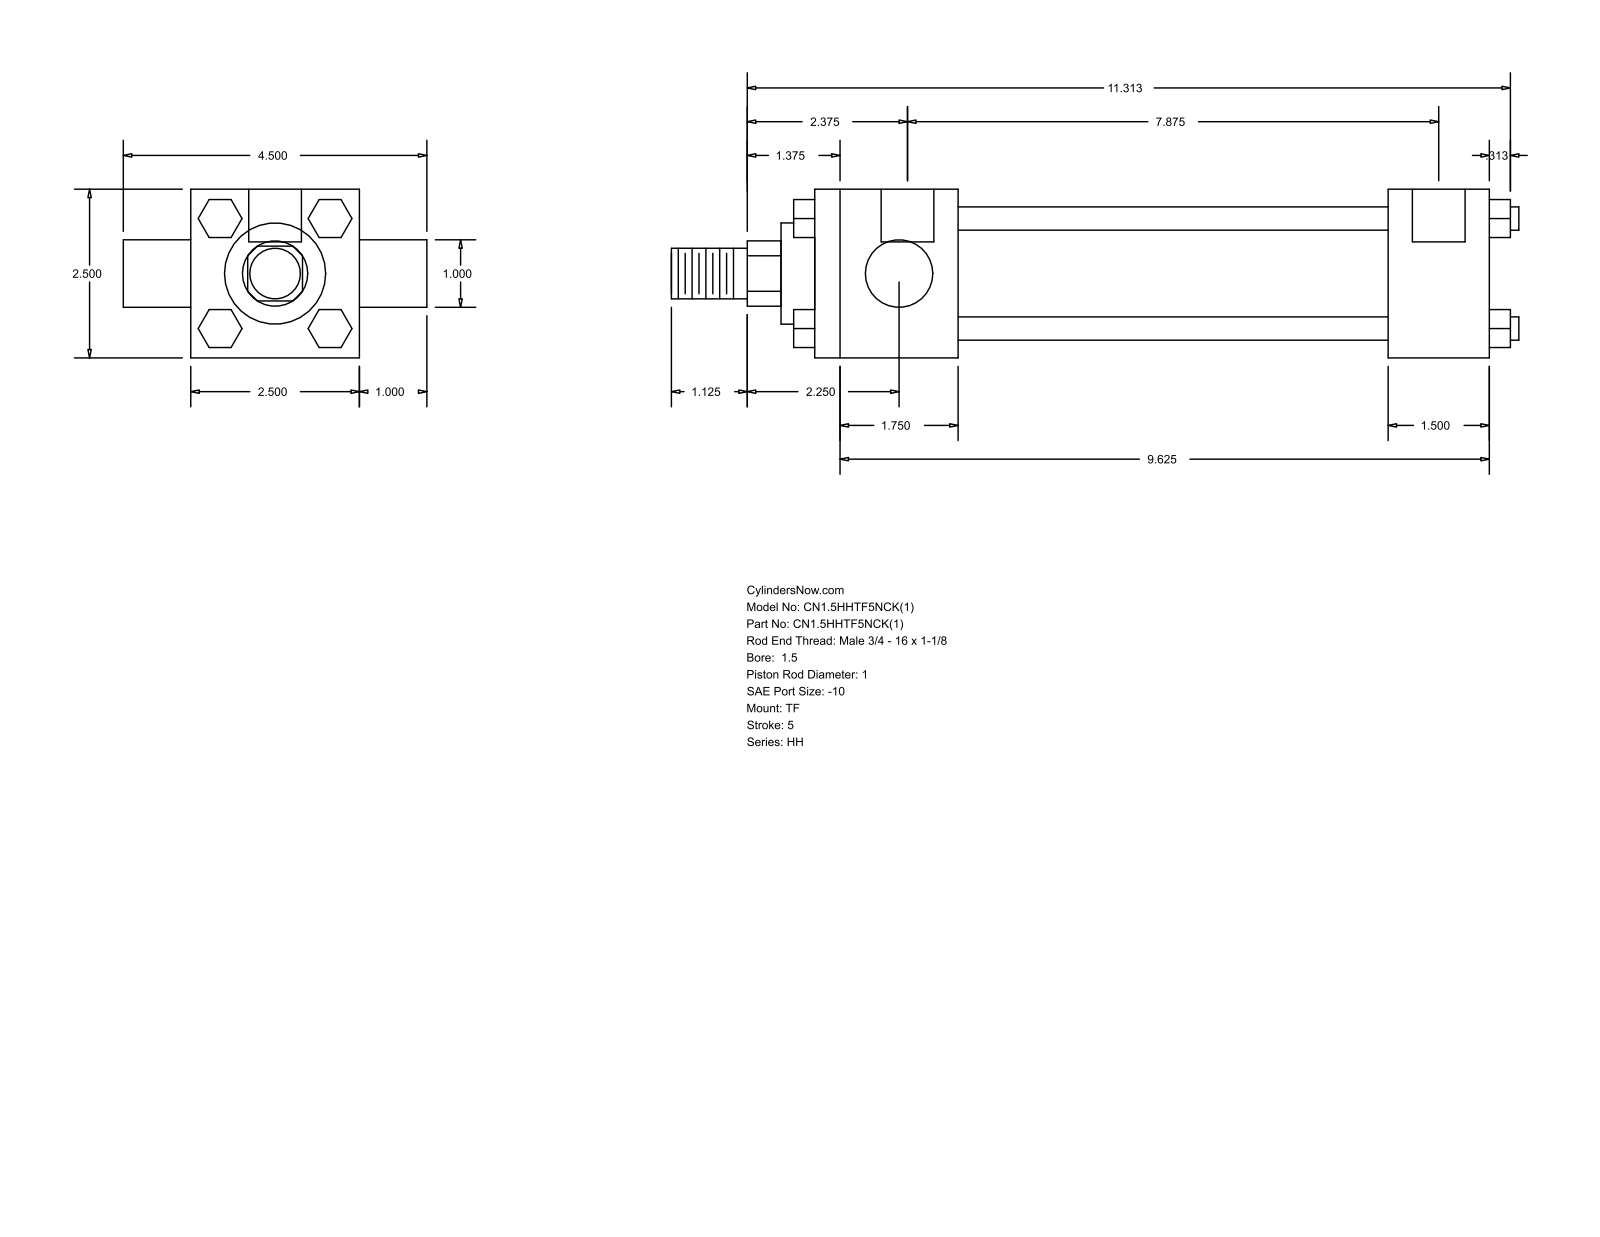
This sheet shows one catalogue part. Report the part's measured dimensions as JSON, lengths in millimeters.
{"part_name": "HH_TF__0150_1", "step_written_by": "GSSL Pune (CONFIG_CONTROL_DESIGN)", "units": "millimeters", "bodies": {"solids": 0, "faces": 120, "planar": 92, "cylindrical": 28, "other": 0}, "overall_size": [319.09, 114.3, 63.5], "round_holes": [[5.56, 3], [19.84, 2]], "round_bosses_or_shafts": [[8.76, 4], [25.4, 2], [44.45, 1], [38.1, 1], [19.05, 1]], "partial_cylinders_radius": [[12.29, 1]], "face_to_face_distances": [63.5, 38.1, 200.02, 161.92, 53.98, 215.9, 254, 25.4, 20.7, 14.29], "hole_center_spacings": [1.59, 201.61, 200.02, 203.2]}
